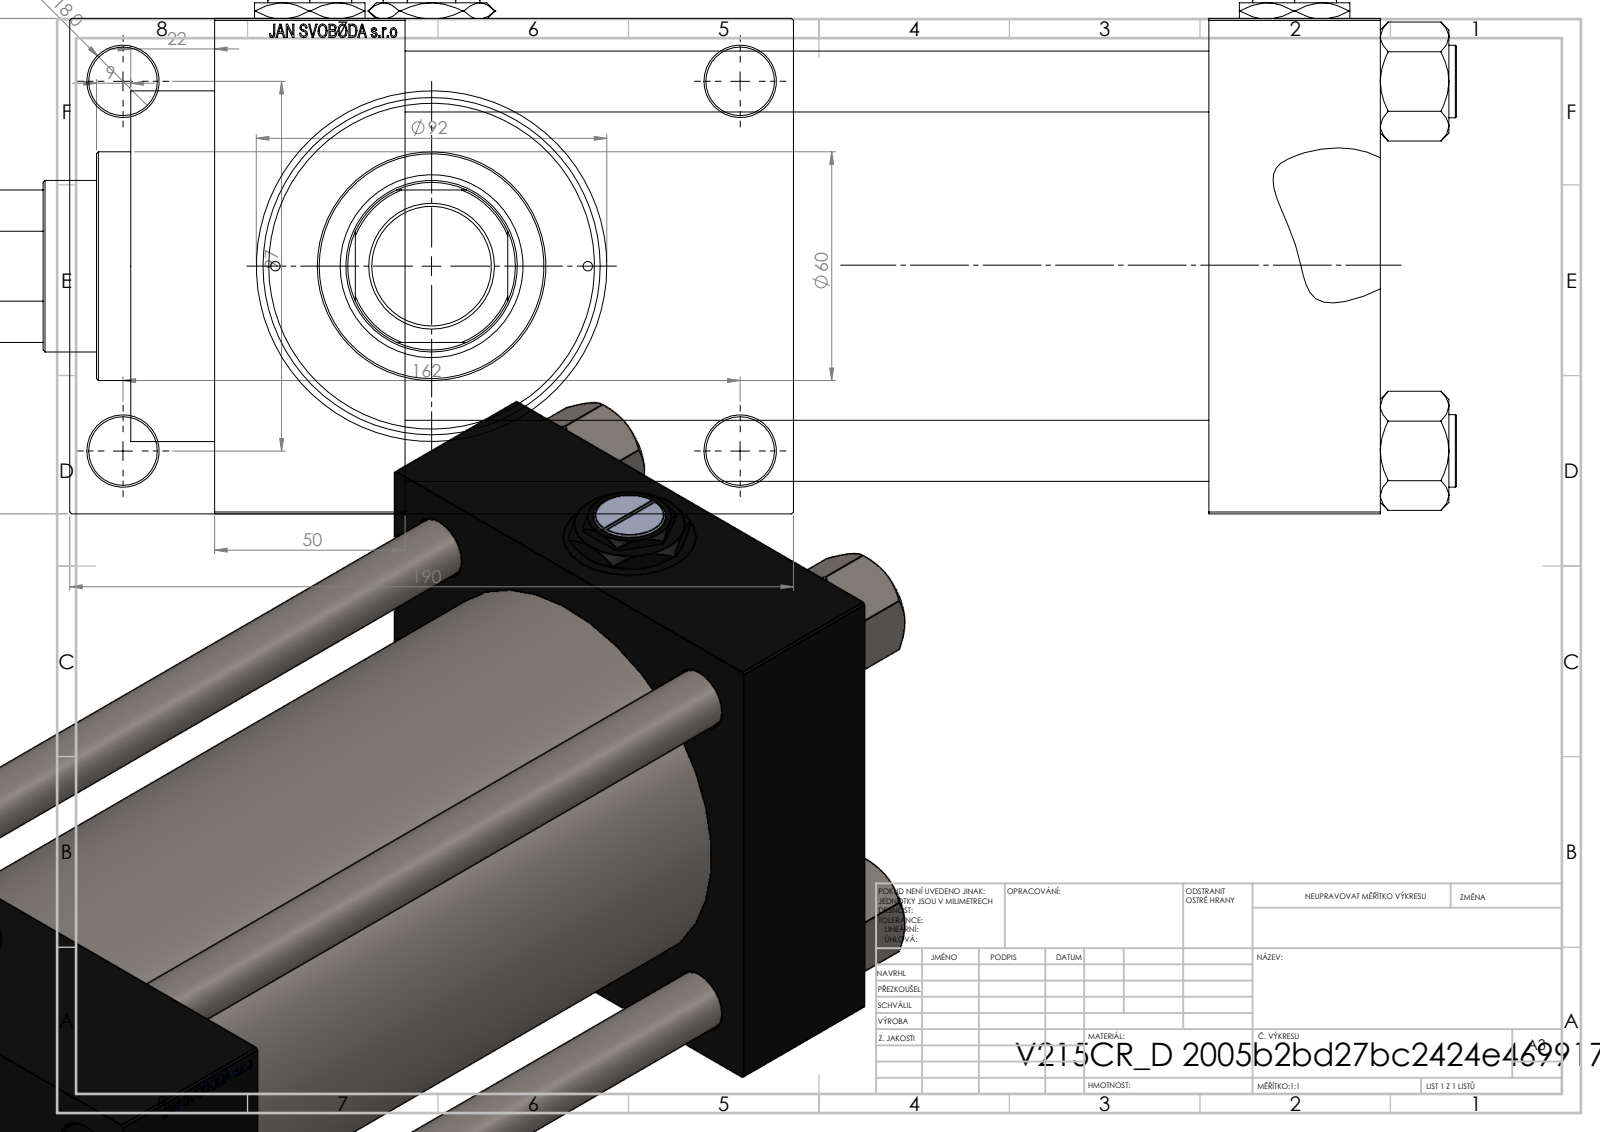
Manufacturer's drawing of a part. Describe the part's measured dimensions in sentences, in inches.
The part is named "Zatka_pro_OIL_PORT; V215CR_D_TYCINKA; V215CR_D_Body; NUT_M5_D (+3 more)". Its 3-D file was written by "SolidWorks 2019 (CONFIG_CONTROL_DESIGN)". It is 14 solids with 1274 faces: 599 planar, 107 cylindrical and 568 other. Overall it measures 16.85 by 7.48 by 5.394 inches. Its volume is 188.3 cubic inches and its surface area 785.3 square inches. Round holes: 4 of diameter 0.63, 4 of diameter 0.709, 4 of diameter 1.041, 4 of diameter 1.378, 3 of diameter 0.276, 2 of diameter 0.098, 1 of diameter 1.24, 1 of diameter 1.772, 1 of diameter 1.89, 1 of diameter 2.992, 1 of diameter 3.366, 1 of diameter 3.937. Round bosses or shafts: 4 of diameter 0.748, 1 of diameter 4.173, 1 of diameter 3.622, 1 of diameter 2.362, 1 of diameter 1.299, 1 of diameter 1.22. Partial cylindrical surfaces (rounded edges, fillets, slot ends): 1 of radius 0.866. The main face-to-face distances are 1.772, 5.118, 10.079, 8.307, 12.047, 10.276, 1.969, 6.299, 1.181, 3.78. The hole center spacings are 1.281, 1.93, 2.475, 2.698, 3.717, 3.815, 4.005, 4.026.
